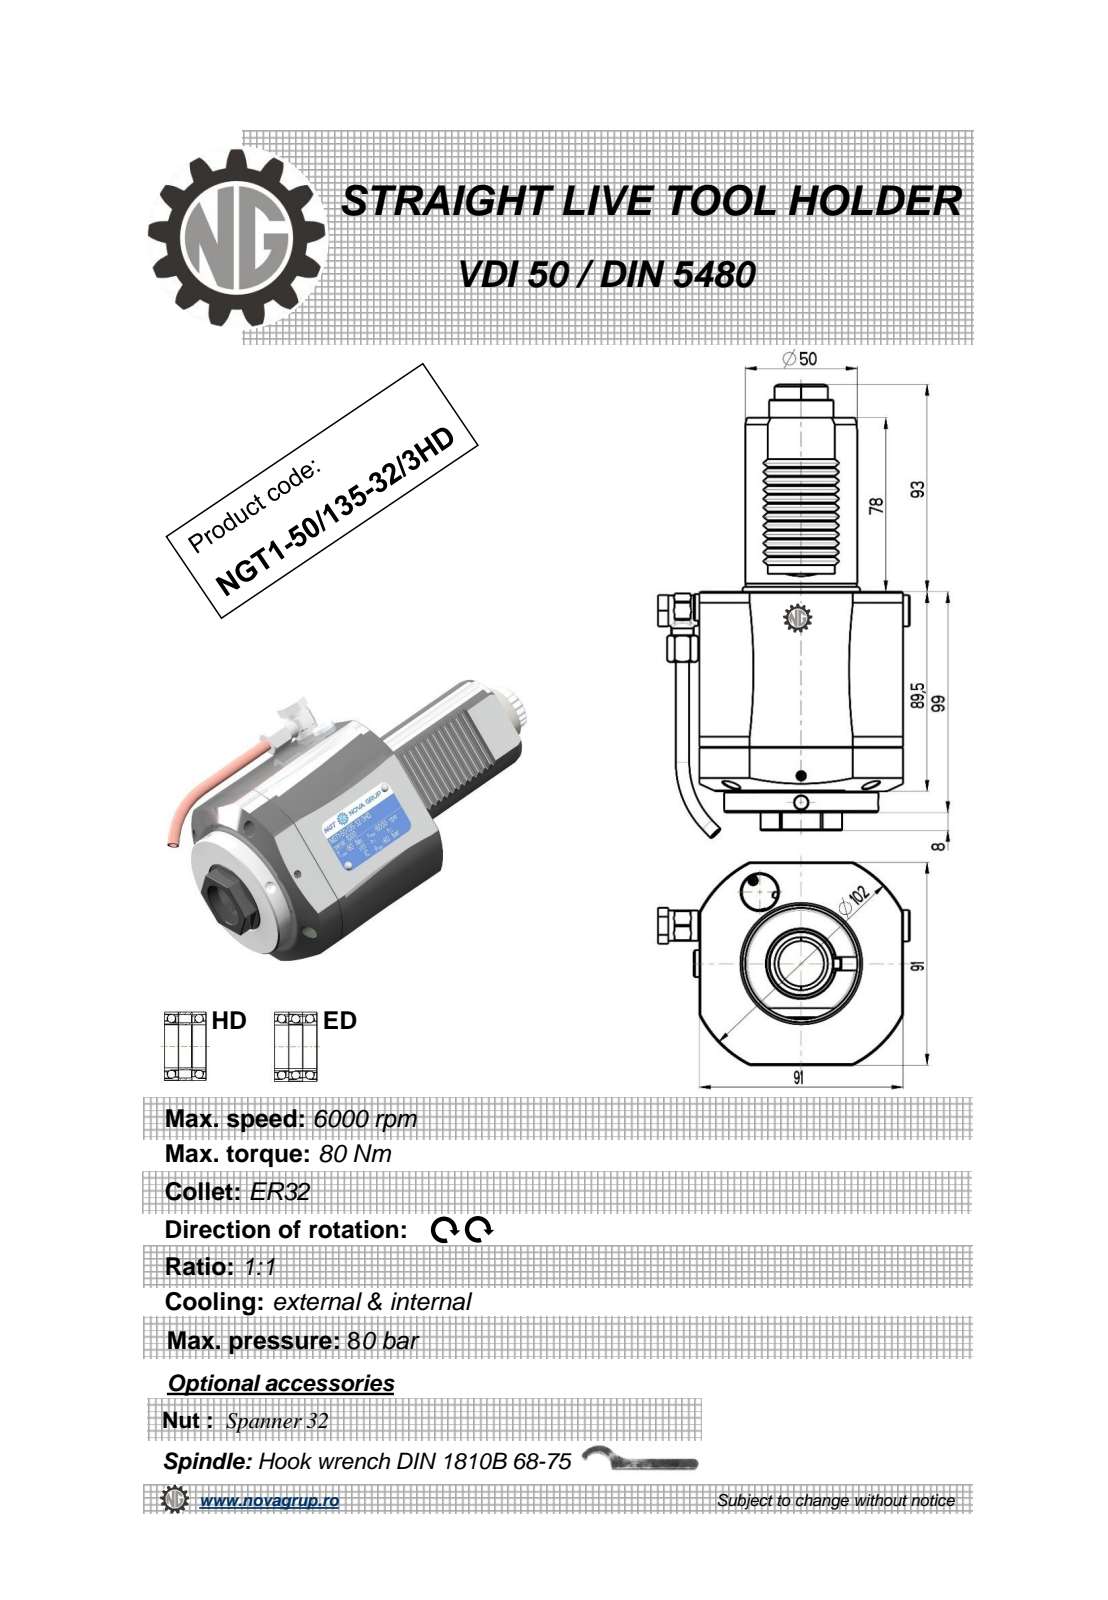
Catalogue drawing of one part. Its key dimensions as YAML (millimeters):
part_name: "NGT1_50_135_32_3HD"
step_written_by: "PRO/ENGINEER BY PARAMETRIC TECHNOLOGY CORPORATION, 2010280 (CONFIG_CONTROL_DESIGN)"
units: millimeters
bodies: {solids: 1, faces: 542, planar: 179, cylindrical: 191, other: 172}
overall_size: [203.44, 112.4, 91]
volume: 847805
surface_area: 67803
round_holes:
  - {diameter: 4, count: 3}
  - {diameter: 6, count: 2}
  - {diameter: 3, count: 1}
  - {diameter: 6.2, count: 1}
  - {diameter: 9, count: 1}
  - {diameter: 10, count: 1}
  - {diameter: 11, count: 1}
  - {diameter: 23, count: 1}
  - {diameter: 34, count: 1}
round_bosses_or_shafts:
  - {diameter: 6, count: 2}
  - {diameter: 69, count: 1}
  - {diameter: 50, count: 1}
  - {diameter: 28.8, count: 1}
  - {diameter: 14, count: 1}
  - {diameter: 13.6, count: 1}
  - {diameter: 13, count: 1}
  - {diameter: 12, count: 1}
partial_cylinders:
  - {radius: 3.04, count: 36}
  - {radius: 0.3, count: 12}
  - {radius: 0.41, count: 6}
  - {radius: 0.5, count: 4}
  - {radius: 6.25, count: 1}
  - {radius: 7.7, count: 1}
  - {radius: 10.56, count: 1}
  - {radius: 10.75, count: 1}
face_to_face_distances: [91, 99, 9.5, 89.5, 2.83, 78, 177, 167.5, 14.14, 25.5]
hole_center_spacings: [0.4, 55.66, 56.04, 87.66]
